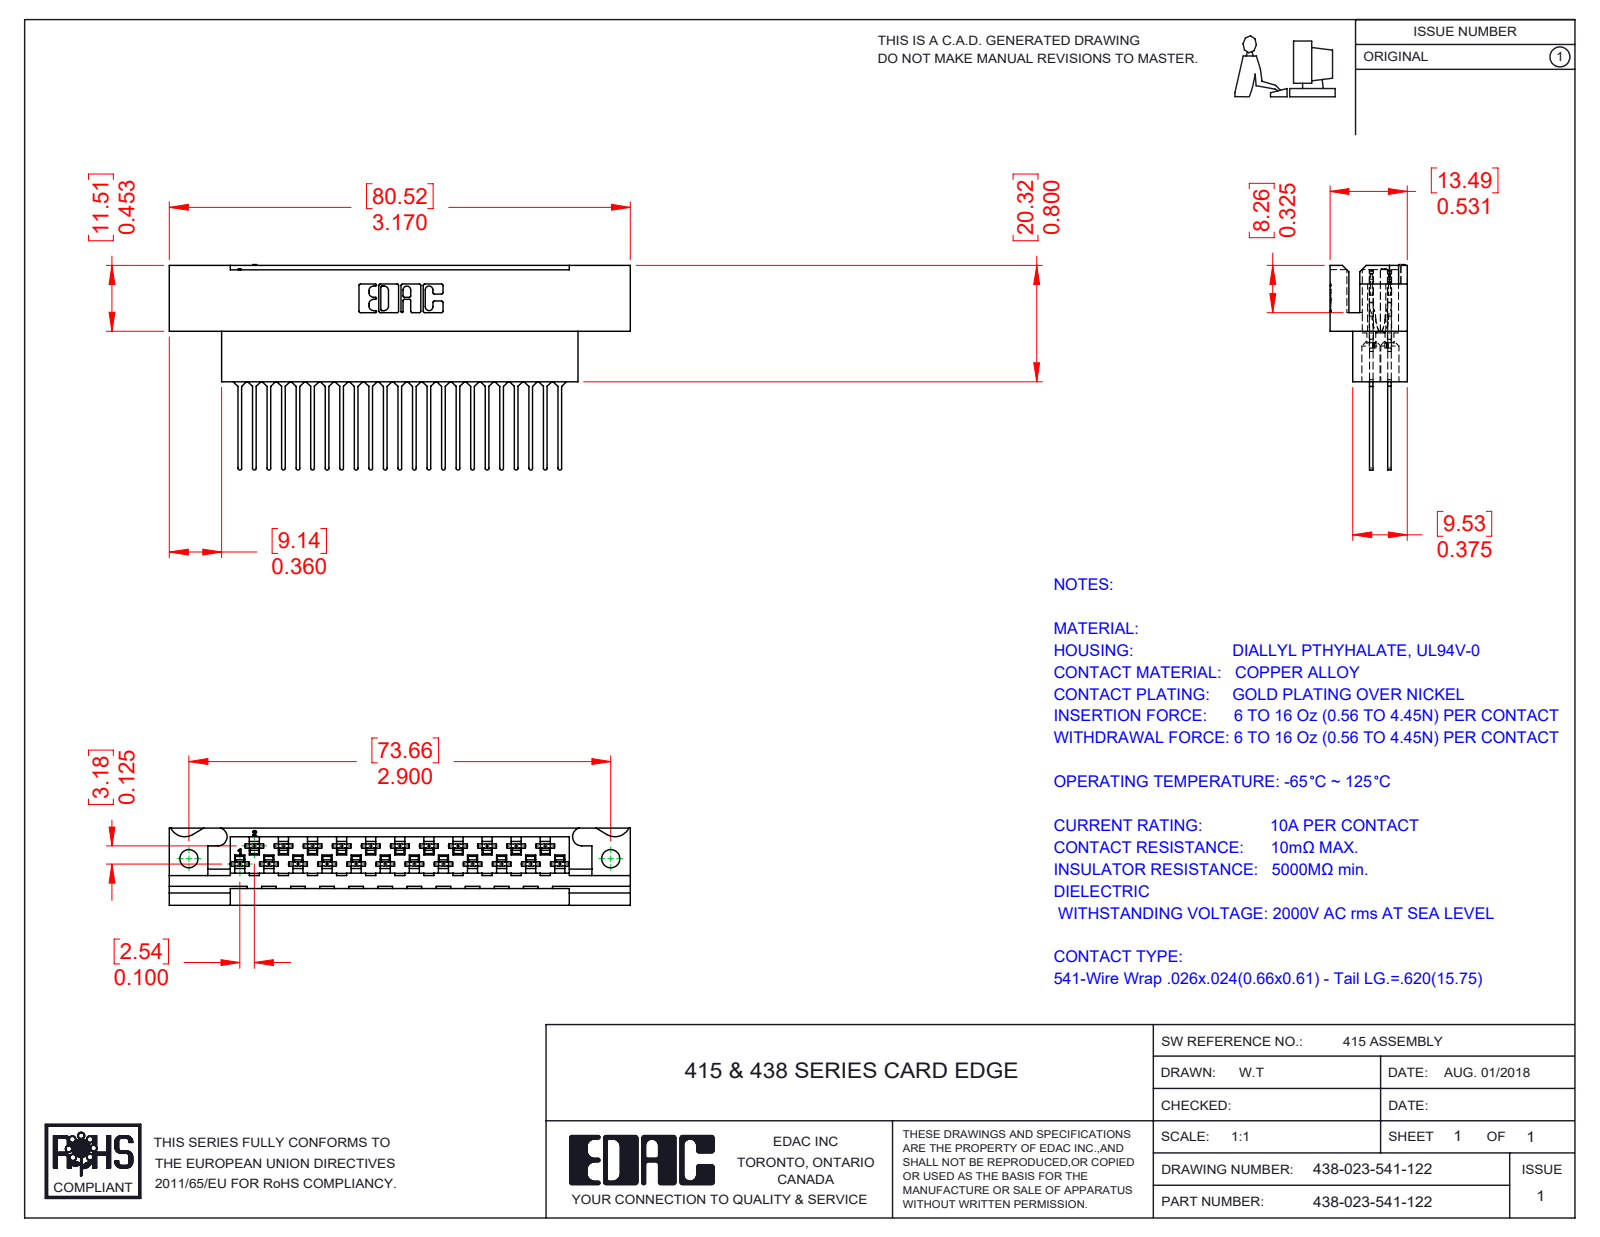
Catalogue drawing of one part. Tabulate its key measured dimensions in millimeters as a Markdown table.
| quantity | value |
| --- | --- |
| part name | 438-210-001_438-210-023-112; 438-023-541-122; 516-290-001_541 |
| STEP written by | SolidWorks 2016 (CONFIG_CONTROL_DESIGN) |
| units | millimeters |
| bodies | 24 solids, 2410 faces (1533 planar, 648 cylindrical, 229 other) |
| overall size | 80.52 × 35.85 × 13.49 |
| volume | 12 992 mm³ |
| surface area | 16 109 mm² |
| round holes (diameter × count) | 1.27 × 23, 3.3 × 23, 3.17 × 1, 3.18 × 1 |
| partial cylindrical surfaces (radius × count) | 0.3 × 92, 0.56 × 92, 0.18 × 46, 0.2 × 46, 0.41 × 46, 2.03 × 46, 0.33 × 23, 0.25 × 22 |
| main face-to-face distances | 3.18, 0.61, 1.88, 1.27, 13.49, 7.49, 2.92, 3.96, 6.61, 6.88 |
| hole center spacings | 5.08, 10.16, 15.24, 20.32, 25.4, 2.54, 4.06, 30.48 |
